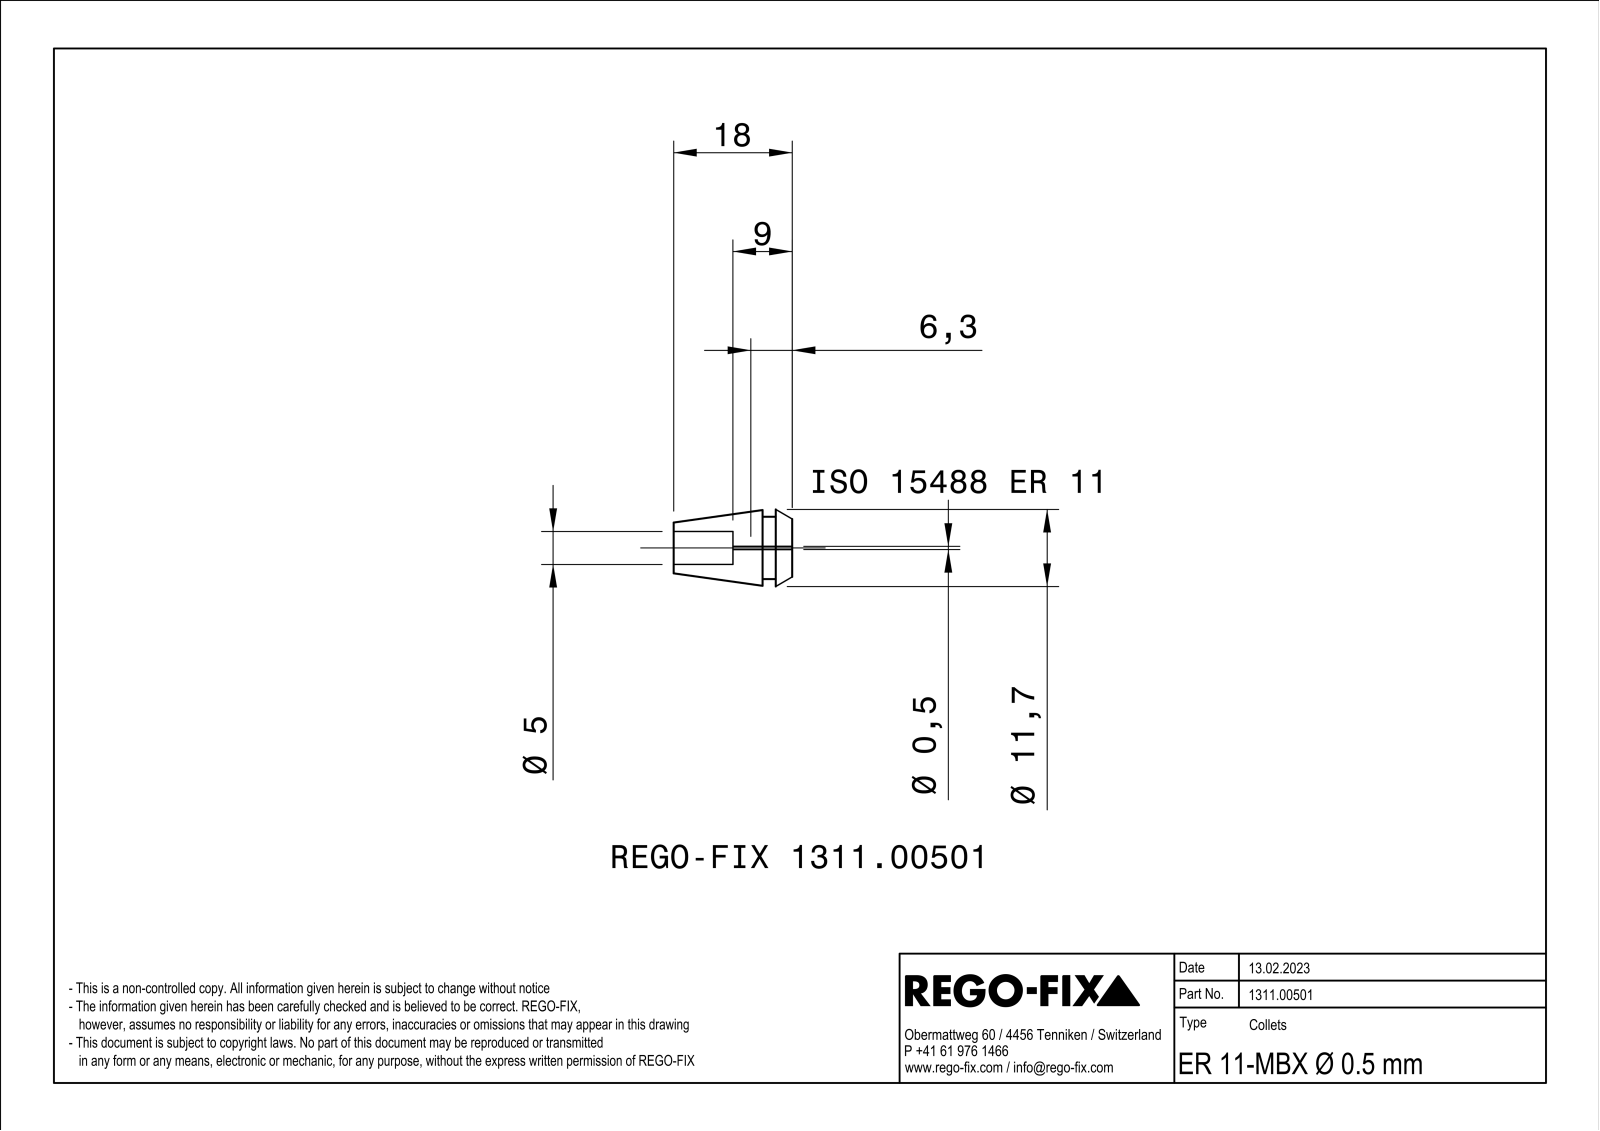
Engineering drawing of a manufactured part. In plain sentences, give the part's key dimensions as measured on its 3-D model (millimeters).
The part is named "NOCUT". Its 3-D file was written by "SIEMENS PLM Software Solid Edge ST10 (AUTOMOTIVE_DESIGN)". It is 1 solid with 91 faces: 26 planar, 19 cylindrical and 46 other. Overall it measures 18 by 11.41 by 11.39 millimeters. Its volume is 992 cubic millimeters and its surface area 1 256 square millimeters. Round holes: 3 of diameter 1.5, 1 of diameter 5. Round bosses or shafts: 1 of diameter 9.5. Partial cylindrical surfaces (rounded edges, fillets, slot ends): 3 of radius 25, 1 of radius 0.25. The main face-to-face distances are 0.8, 0.51, 4.5, 9, 18, 13.5, 2.5, 2, 15.5, 6.5. The hole center spacings are 1.7, 2.94.
